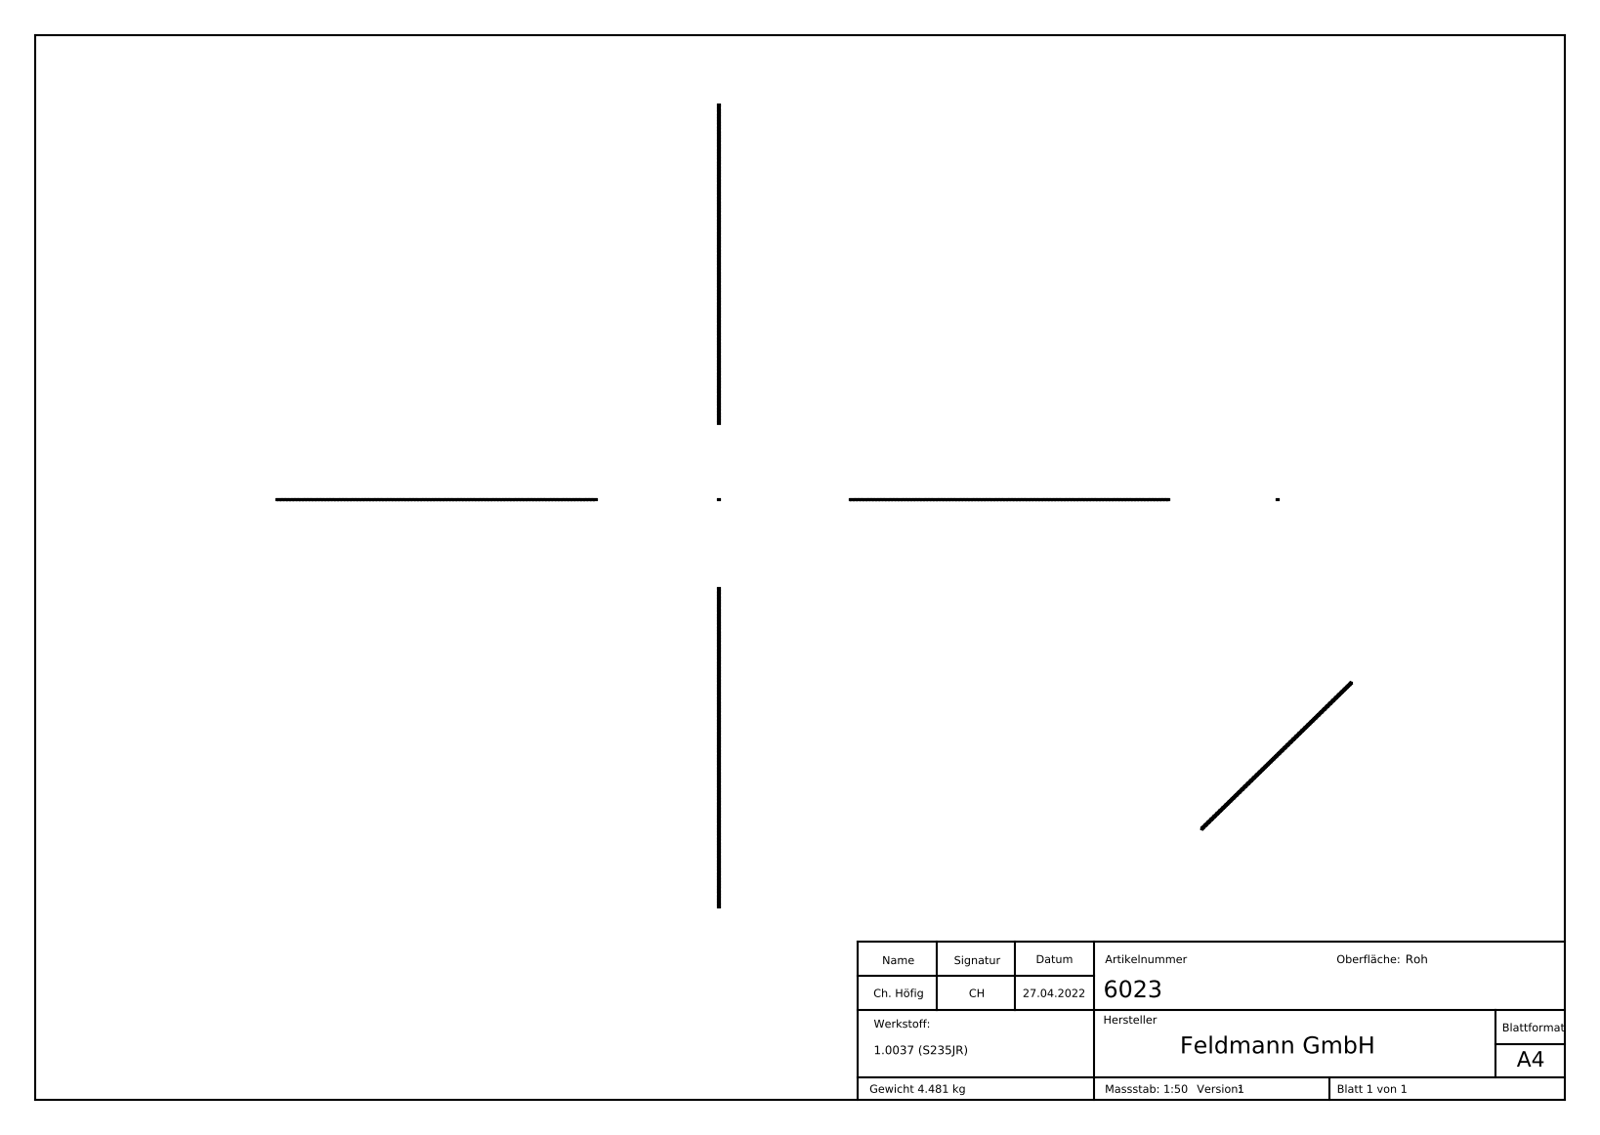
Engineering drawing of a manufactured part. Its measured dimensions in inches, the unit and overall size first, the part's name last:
Units: inches
Overall size (bounding box): 118.11 × 0.551 × 0.551
Main face-to-face distances: 0.551, 118.11, 0.547, 0.139, 0.144, 0.191, 0.013, 0.112, 59.055, 0.236
Volume: 35.06 in³ · Surface area: 254.3 in²
Bodies: 1 solid, 618 faces (112 planar, 0 cylindrical, 506 other)
Part name (STEP PRODUCT): 6023
STEP written by: SolidWorks 2018 (CONFIG_CONTROL_DESIGN)
